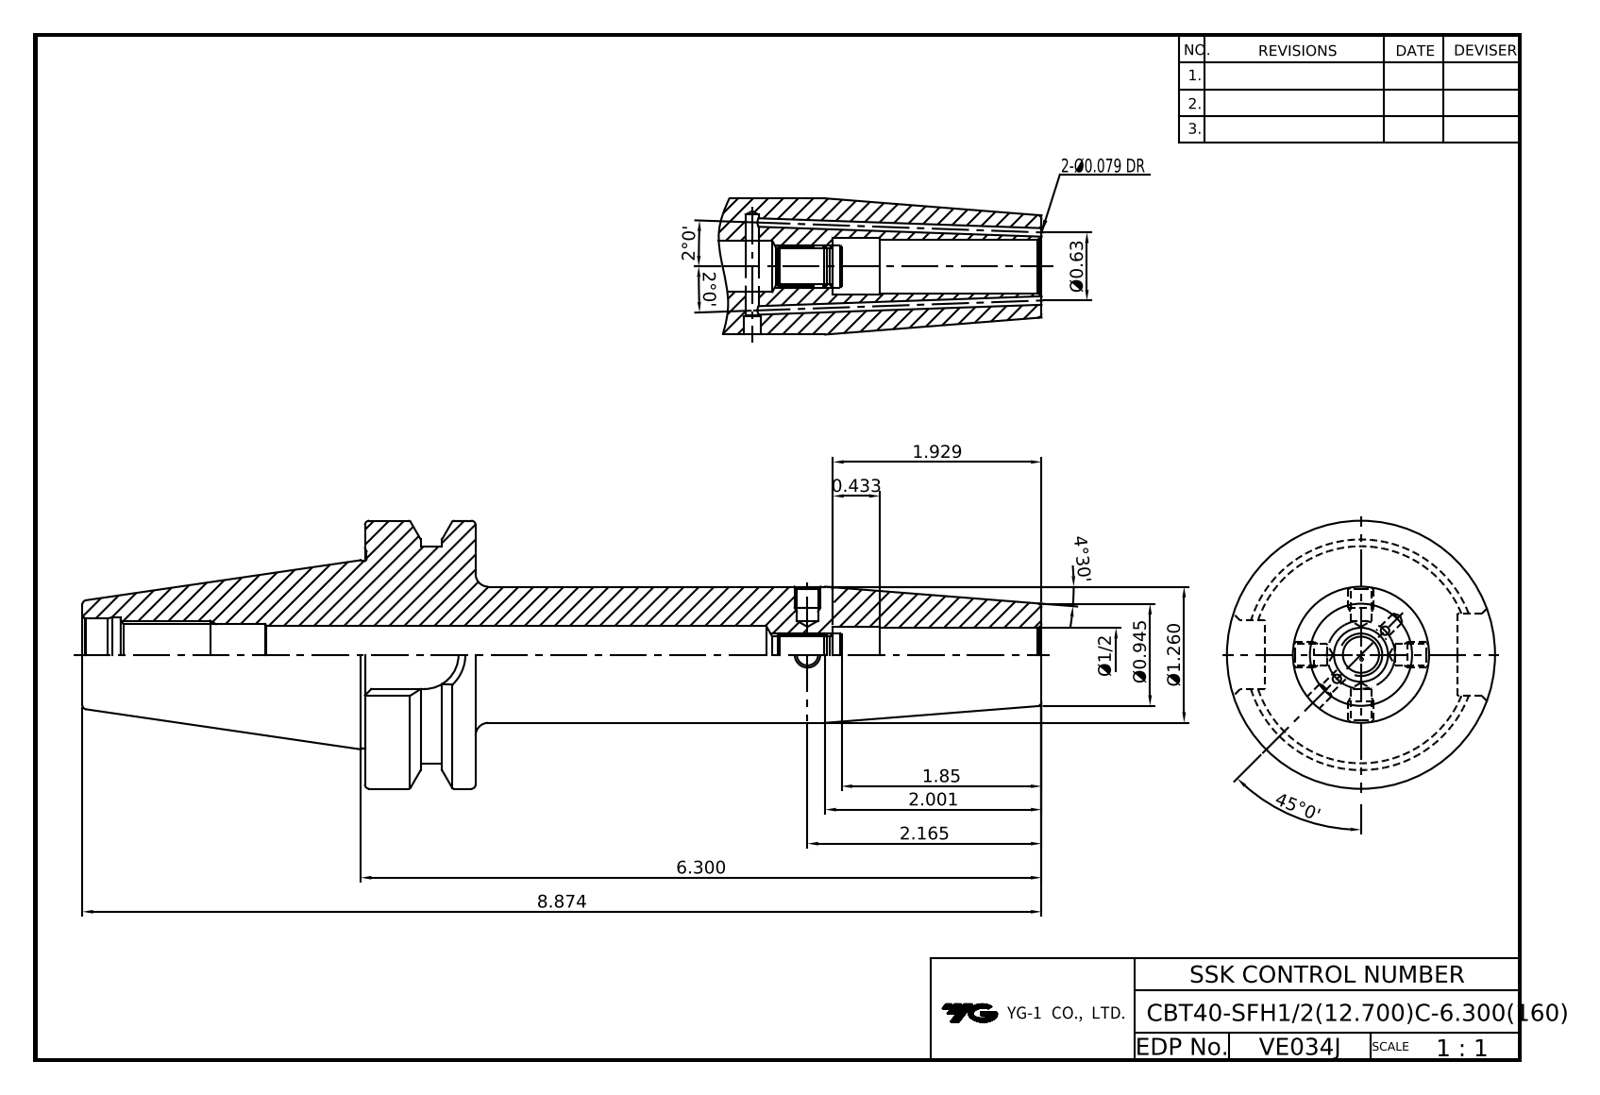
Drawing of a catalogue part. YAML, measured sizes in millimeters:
part_name: "CBT40-SFH12_7C-160"
step_written_by: "CREO PARAMETRIC BY PTC INC, 2018500 (CONFIG_CONTROL_DESIGN)"
units: millimeters
bodies: {solids: 1, faces: 92, planar: 22, cylindrical: 28, other: 42}
overall_size: [225.4, 63, 63]
volume: 199485
surface_area: 41435
round_holes:
  - {diameter: 10, count: 1}
  - {diameter: 12.7, count: 1}
  - {diameter: 13.3, count: 1}
  - {diameter: 13.5, count: 1}
  - {diameter: 14, count: 1}
  - {diameter: 16, count: 1}
  - {diameter: 17, count: 1}
  - {diameter: 17.6, count: 1}
round_bosses_or_shafts:
  - {diameter: 63, count: 1}
  - {diameter: 51, count: 1}
  - {diameter: 44, count: 1}
  - {diameter: 32, count: 1}
partial_cylinders:
  - {radius: 8.05, count: 1}
face_to_face_distances: [25, 45.2, 17.1, 7.9, 158, 140.9, 133, 12.1, 5, 12.9]
